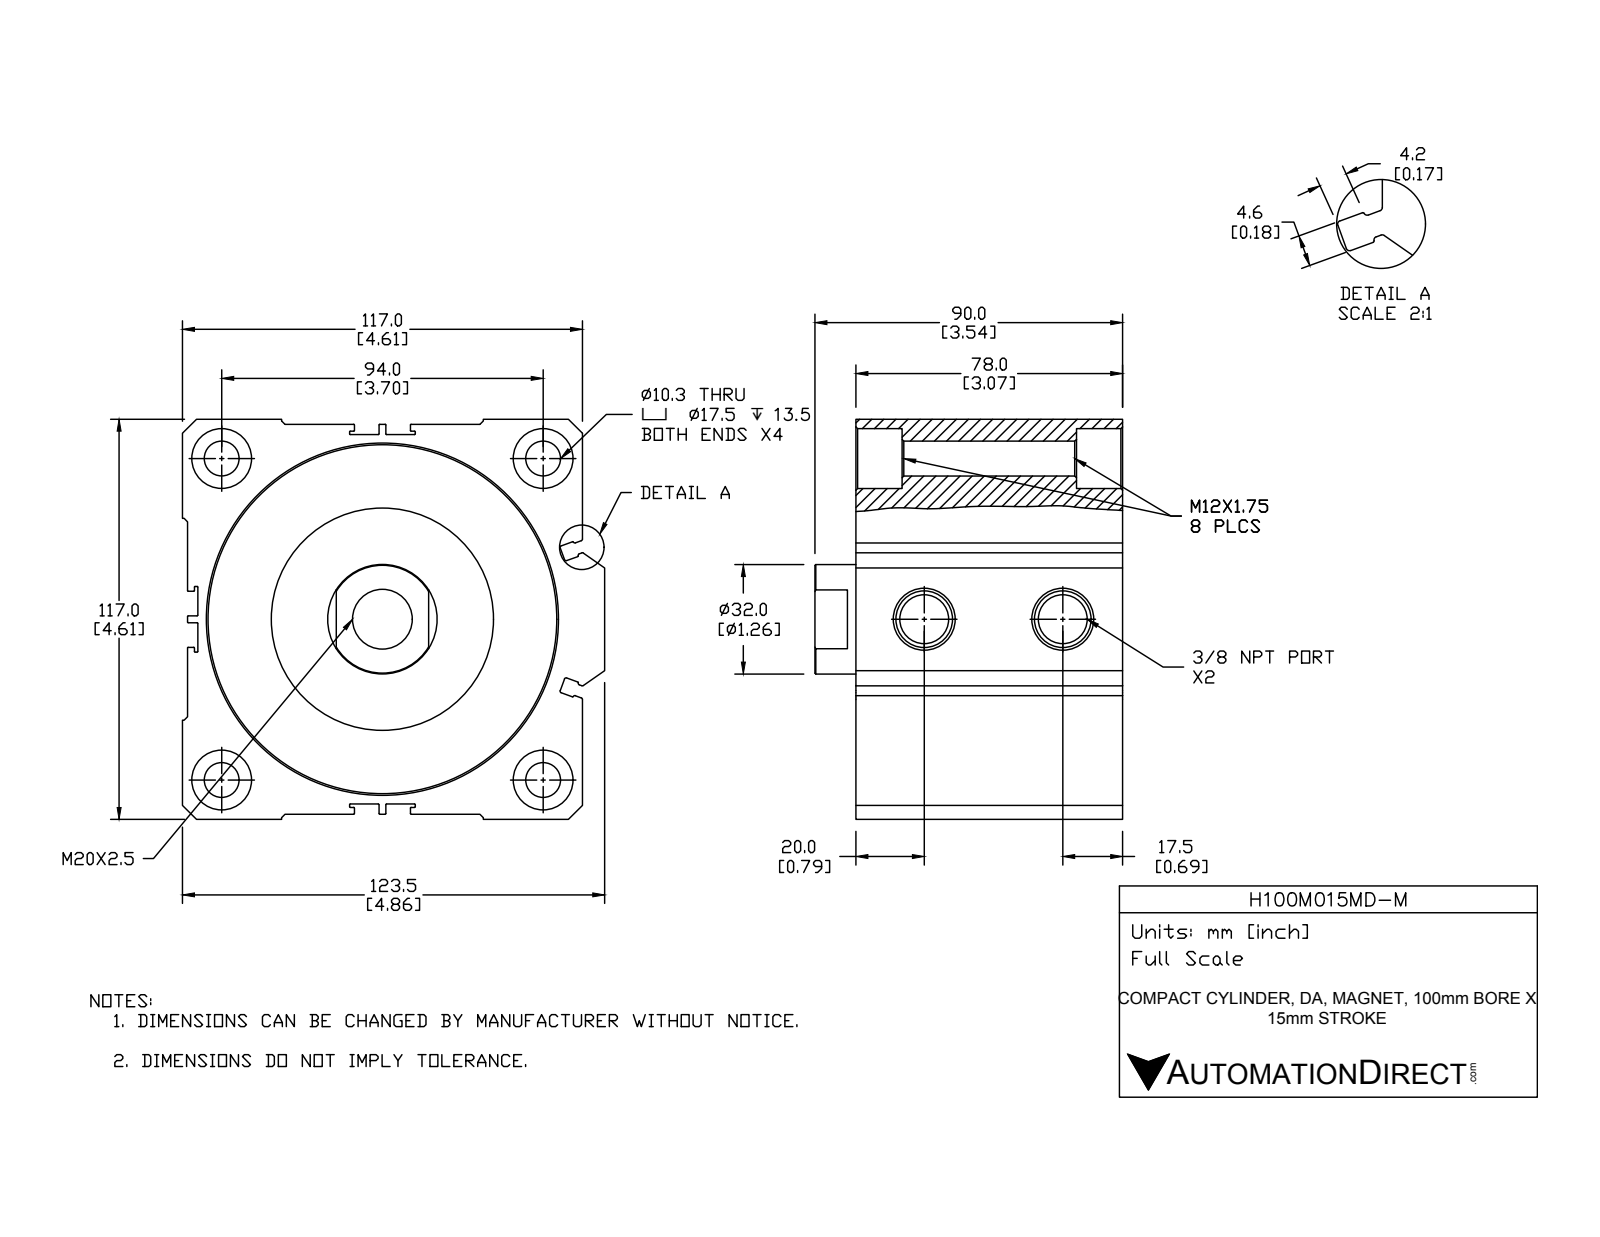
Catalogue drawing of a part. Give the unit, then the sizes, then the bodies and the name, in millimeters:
Units: millimetres
Overall size (bounding box): 123.5 × 117 × 90
Round holes (diameter × count): ⌀17.5 ×5, ⌀10.2 ×4, ⌀14.27 ×2, ⌀32 ×1, ⌀65 ×1, ⌀100 ×1, ⌀102 ×1
Round bosses / shafts (diameter × count): ⌀39 ×1
Partial cylindrical surfaces — rounded edges, fillets, slot ends (radius × count): R0.2 ×40, R0.5 ×12
Main face-to-face distances: 115.5, 1.5, 117, 43.5, 56, 27.8, 15.7, 12.5, 40.3, 12
Hole centre spacings: 66.47, 94, 132.94, 40.5
Volume: 826 997 mm³ · Surface area: 148 686 mm²
Bodies: 2 solids, 261 faces (105 planar, 103 cylindrical, 53 other)
Part name (STEP PRODUCT): H100M015MD-M-BODY; H100M015MD-M; H100M015MD-M-PISTON
STEP written by: SolidWorks 2015 (CONFIG_CONTROL_DESIGN)
